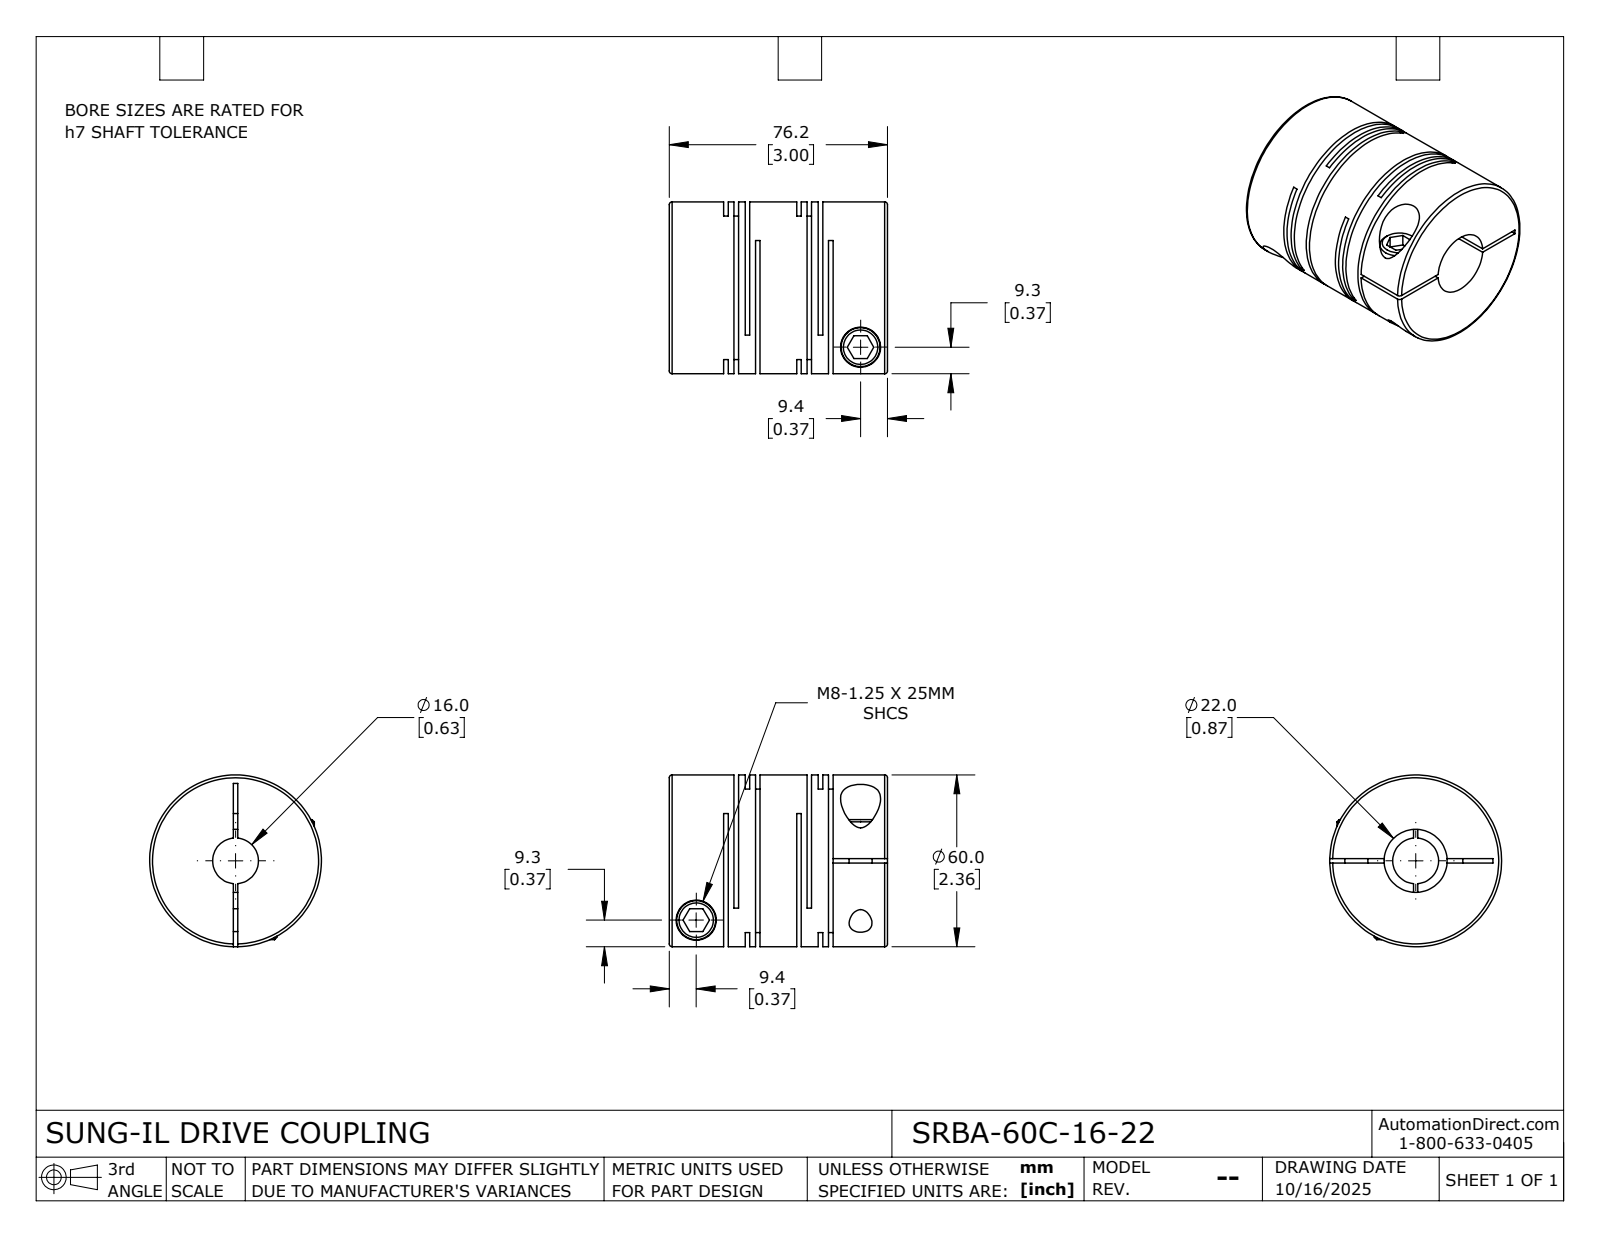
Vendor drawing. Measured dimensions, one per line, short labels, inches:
name: SRBA-60C-16-22
written by: SolidWorks 2024 (CONFIG_CONTROL_DESIGN)
unit: in
bodies: 1 solid, 115 faces (60 planar, 42 cylindrical, 13 other)
size: 3 × 2.362 × 2.362
volume: 9.73 in³; area: 90.52 in²
holes: 2× ⌀0.315, 2× ⌀0.551, 1× ⌀0.63, 1× ⌀0.866
bosses: 2× ⌀0.535, 1× ⌀2.362
face distances: 0.063, 0.142, 0.295, 1.004, 1.299, 0.079, 0.232, 0.154, 0.941, 0.862
